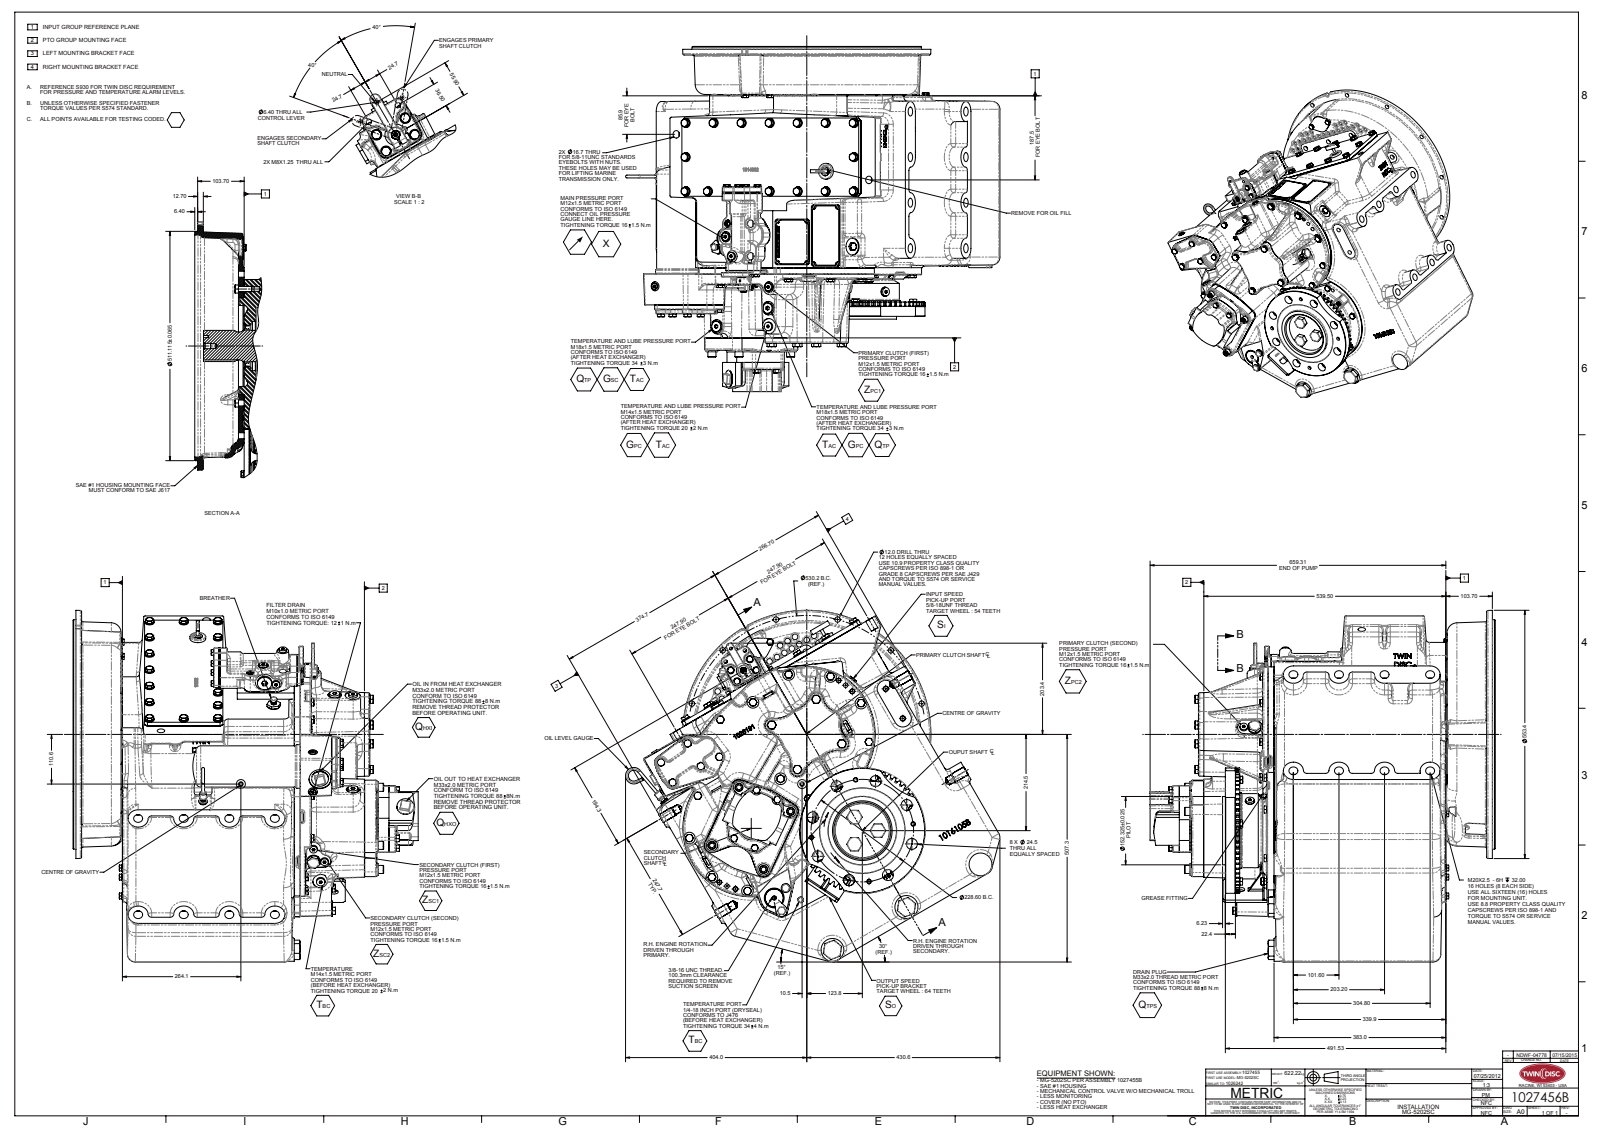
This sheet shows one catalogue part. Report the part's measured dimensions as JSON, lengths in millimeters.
{"part_name": "1027456B", "step_written_by": "SolidWorks 2010 (AUTOMOTIVE_DESIGN)", "units": "millimeters", "bodies": {"solids": 0, "faces": 4372, "planar": 1231, "cylindrical": 1359, "other": 1782}, "overall_size": [834.6, 783.96, 769.41], "round_holes": [[12.7, 24], [20, 18], [12, 15], [13.5, 14], [24.5, 8], [10, 7], [6.8, 6], [16.5, 4], [8, 3], [11, 2], [16.67, 2], [30, 2]], "round_bosses_or_shafts": [[20, 17], [18, 8], [17, 7], [13.6, 6], [13, 5], [15.32, 4], [16, 3], [6.35, 3]], "partial_cylinders_radius": [[46.33, 89], [3, 80], [7.87, 72], [3.05, 58], [12, 49], [17.53, 33], [1.52, 32], [6.4, 25]], "face_to_face_distances": [12.7, 0.39, 13.58, 397, 13.97, 409.7, 383.03, 395.73, 0.64, 13.33], "hole_center_spacings": [101.6, 203.2, 114.3, 267.68, 247.65, 44.6, 190.07, 304.8]}
